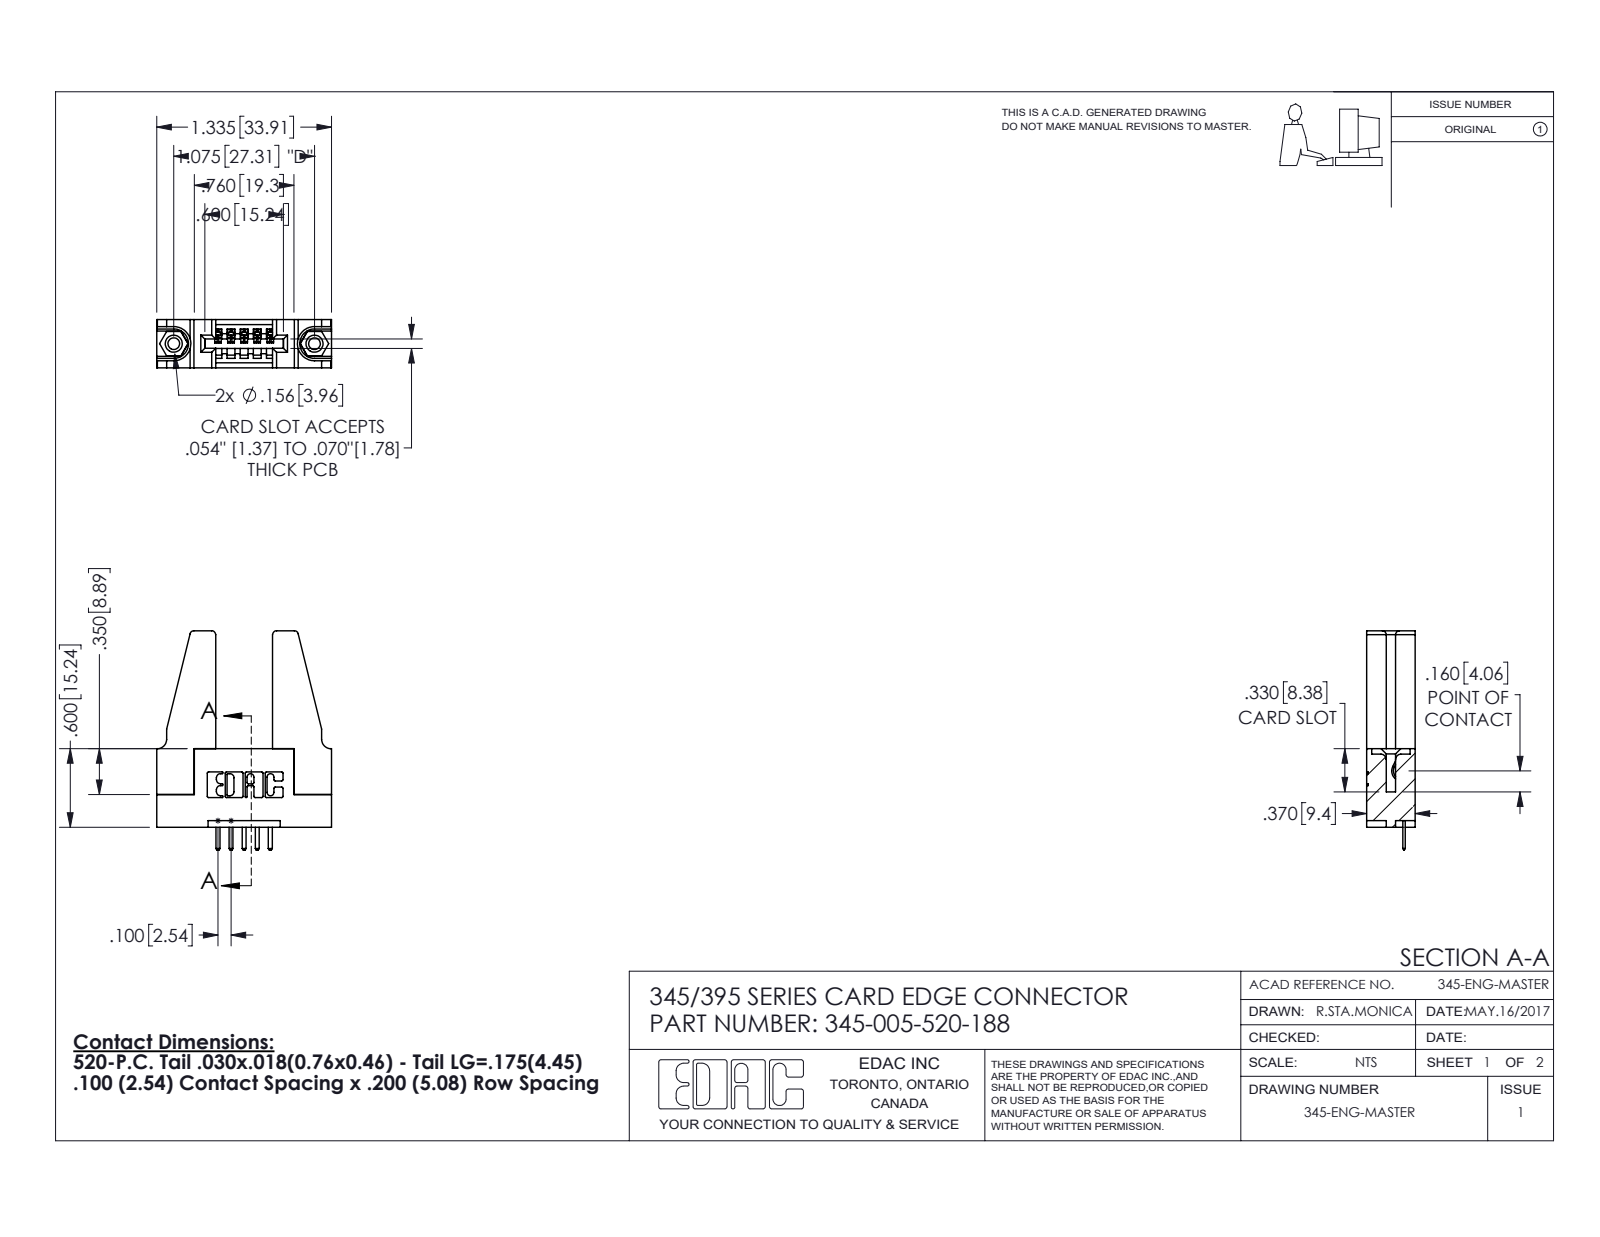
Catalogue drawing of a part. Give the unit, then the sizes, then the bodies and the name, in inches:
Units: inches
Overall size (bounding box): 1.675 × 1.336 × 0.37
Round holes (diameter × count): ⌀0.089 ×2, ⌀0.125 ×2, ⌀0.156 ×2, ⌀0.064 ×1
Round bosses / shafts (diameter × count): ⌀0.155 ×2
Partial cylindrical surfaces — rounded edges, fillets, slot ends (radius × count): R0.01 ×22, R0.01 ×12, R0.006 ×10, R0.03 ×8, R0.007 ×6, R0.031 ×6, R0.026 ×3, R0.031 ×2
Main face-to-face distances: 0.37, 0.2, 0.072, 0.298, 0.598, 0.25, 0.148, 0.15, 0.35, 0.077
Hole centre spacings: 0.27, 0.847, 1.075
Volume: 0.376 in³ · Surface area: 9.983 in²
Bodies: 10 solids, 560 faces (362 planar, 182 cylindrical, 16 other)
Part name (STEP PRODUCT): 345-250-001_345-250-001-102; 345 Part_Flush Mounting Lugs - 0.156 Dia-TH; 345-220-078_345-220-088; 345-292-001_345-293-120 (+1 more)
STEP written by: SolidWorks 2016 (CONFIG_CONTROL_DESIGN)
